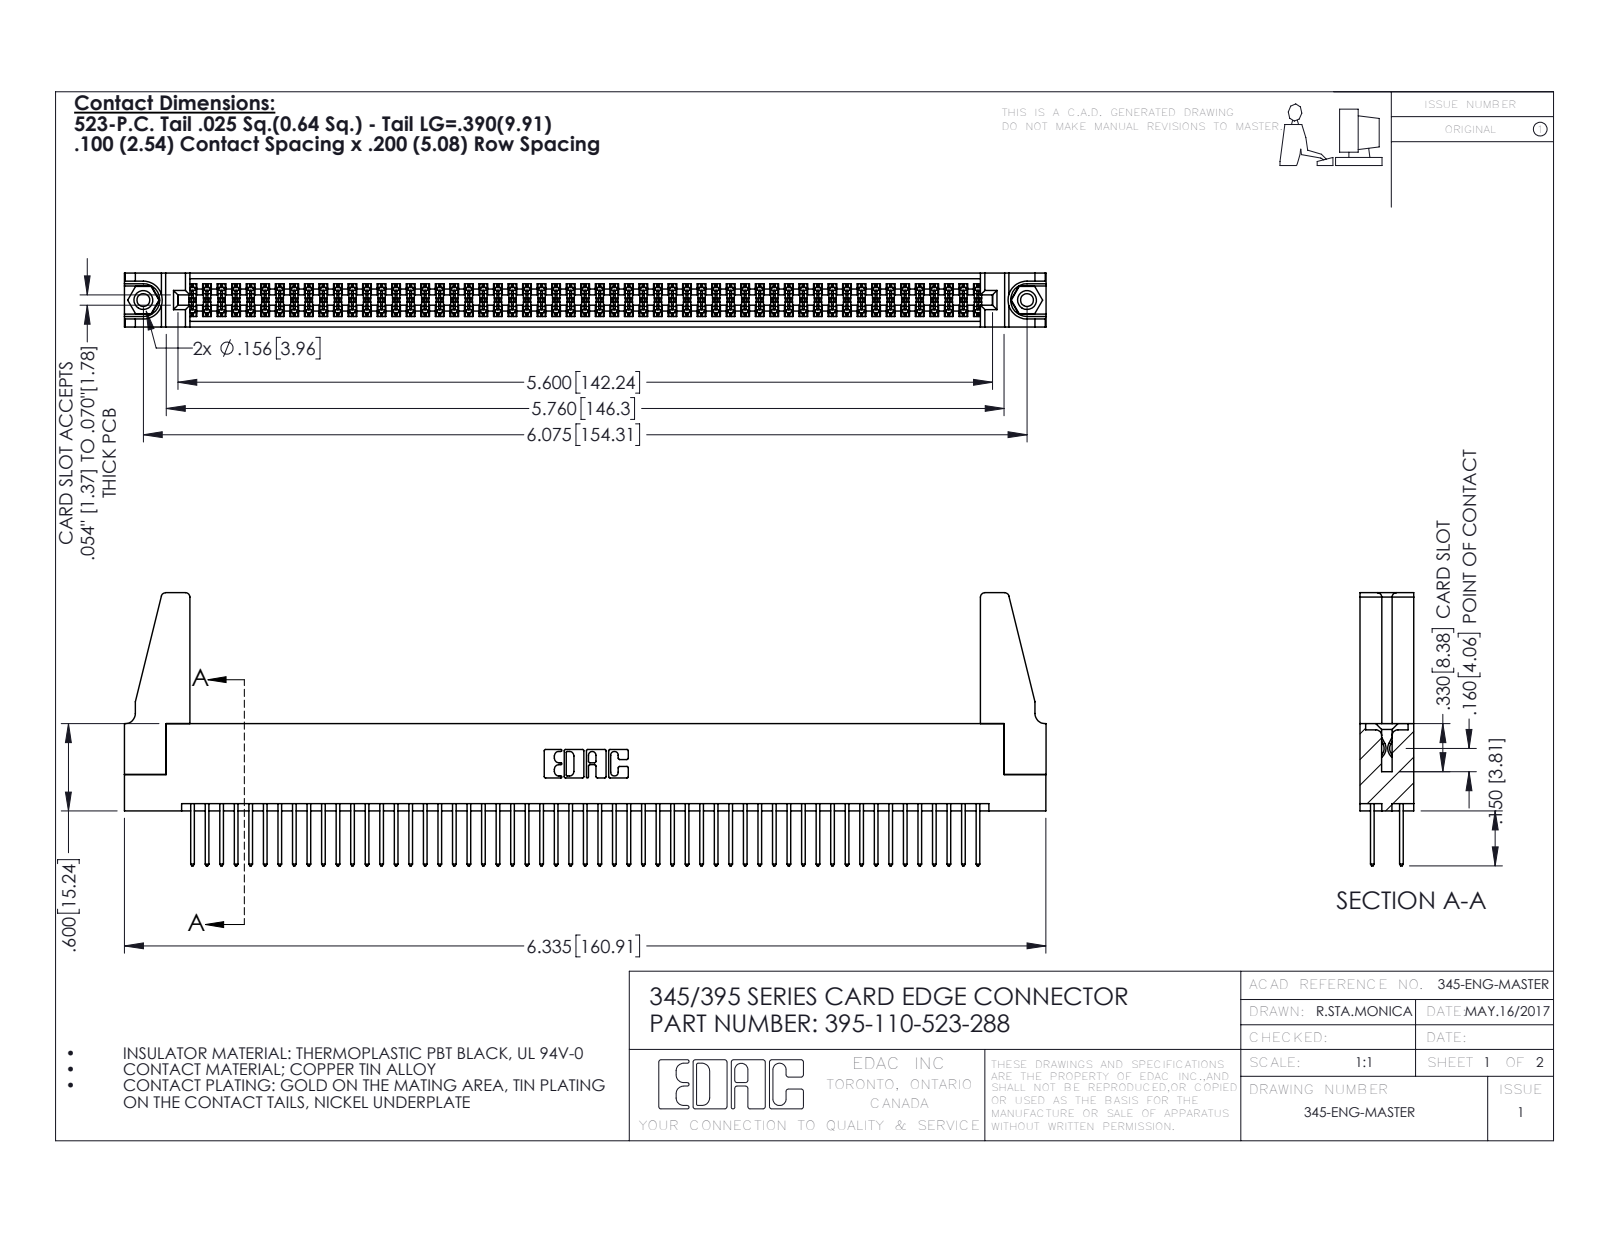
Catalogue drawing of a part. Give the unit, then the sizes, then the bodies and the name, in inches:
Units: inches
Overall size (bounding box): 6.336 × 1.877 × 0.37
Round holes (diameter × count): ⌀0.089 ×2, ⌀0.125 ×2, ⌀0.156 ×2, ⌀0.064 ×1
Round bosses / shafts (diameter × count): ⌀0.155 ×2
Partial cylindrical surfaces — rounded edges, fillets, slot ends (radius × count): R0.006 ×165, R0.01 ×110, R0.01 ×22, R0.03 ×8, R0.007 ×6, R0.031 ×6, R0.026 ×3, R0.014 ×2
Main face-to-face distances: 0.072, 0.298, 0.2, 0.37, 0.098, 0.272, 0.025, 0.225, 0.175, 0.149
Hole centre spacings: 0.27, 5.839, 6.075
Volume: 1.174 in³ · Surface area: 43.41 in²
Bodies: 115 solids, 5750 faces (3782 planar, 1952 cylindrical, 16 other)
Part name (STEP PRODUCT): 345-220-078_345-220-088; 395-110-523-288; 345-250-001_345-250-001-102; 345 Part_Flush Mounting Lugs - 0.156 Dia-TH (+1 more)
STEP written by: SolidWorks 2016 (CONFIG_CONTROL_DESIGN)
